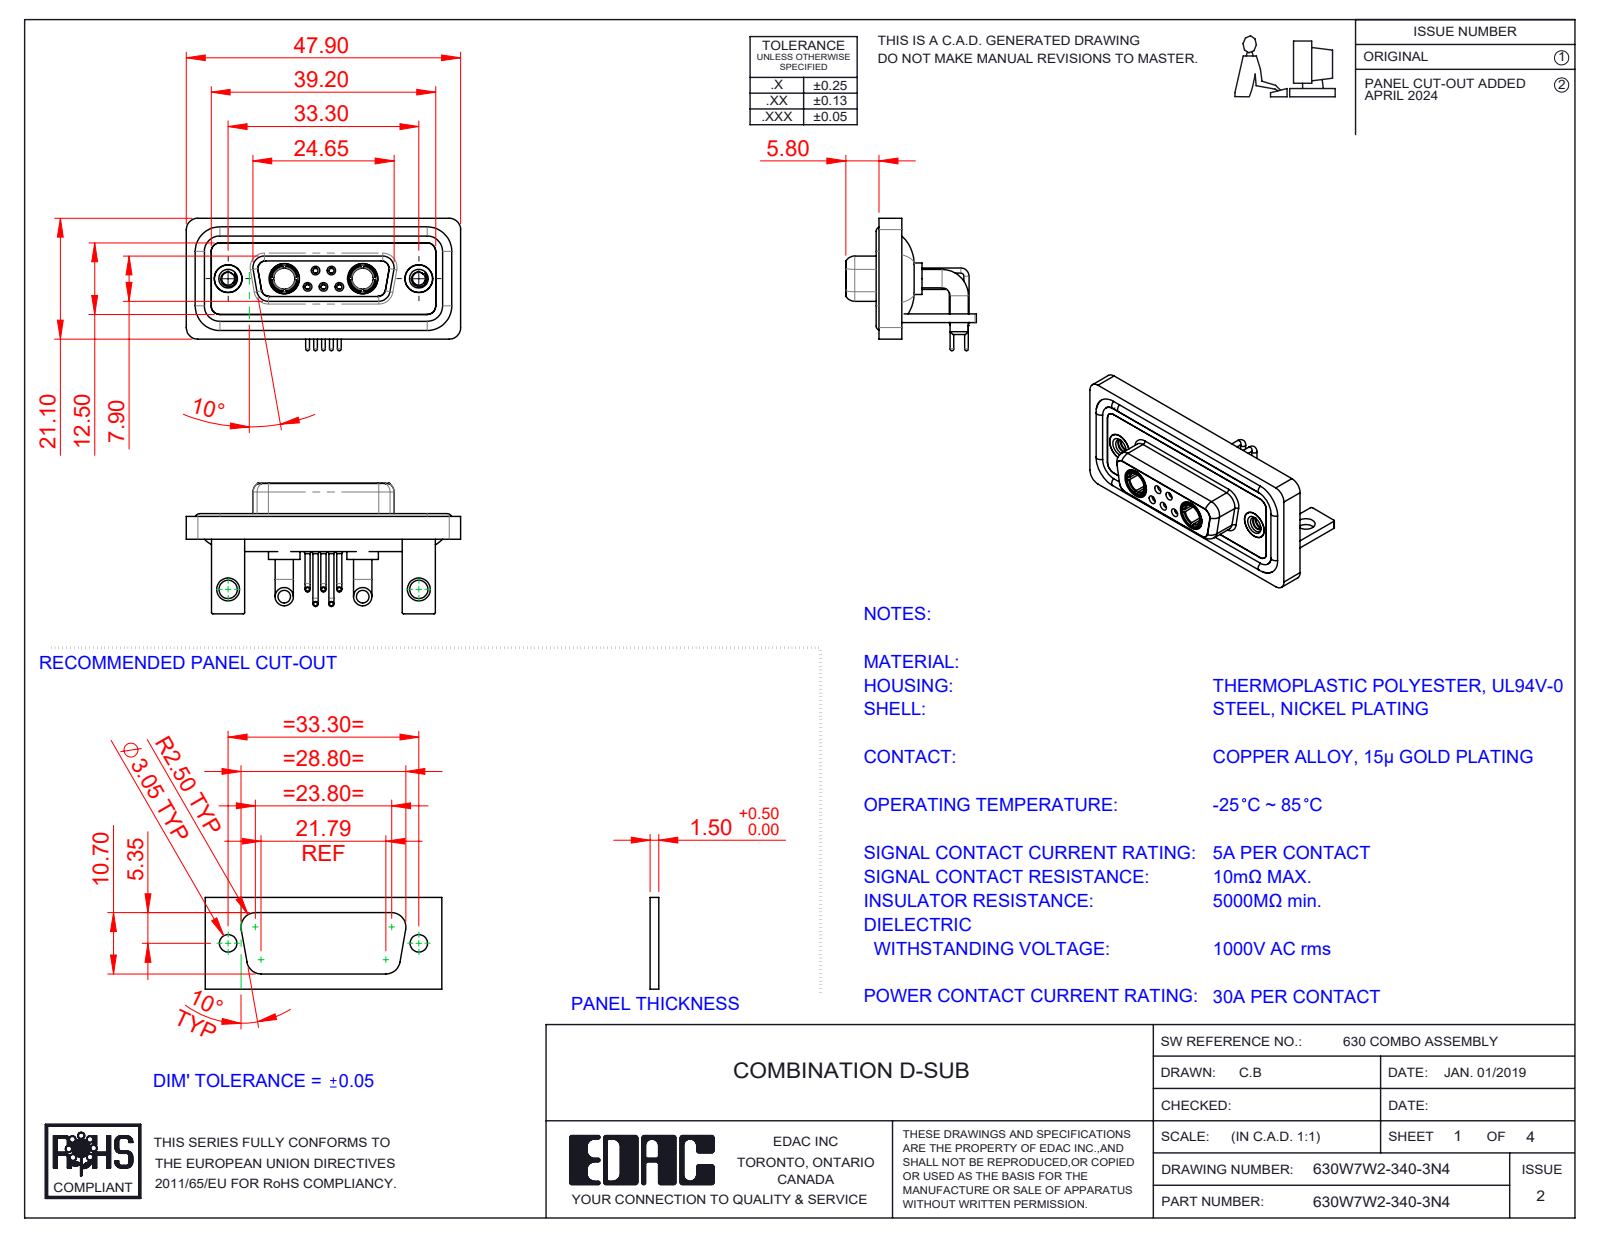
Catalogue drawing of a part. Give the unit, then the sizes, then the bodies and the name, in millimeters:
Units: millimetres
Overall size (bounding box): 47.9 × 23.12 × 22.8
Round holes (diameter × count): ⌀0.9 ×5, ⌀1.1 ×5, ⌀1.5 ×5, ⌀2 ×5, ⌀4.85 ×4, ⌀1.6 ×3, ⌀1.7 ×2, ⌀2.26 ×2, ⌀3.2 ×2, ⌀3.7 ×2, ⌀4 ×2, ⌀4.05 ×2
Round bosses / shafts (diameter × count): ⌀1.6 ×6, ⌀0.9 ×5, ⌀0.65 ×5, ⌀3.2 ×4, ⌀5.5 ×2, ⌀5.2 ×2, ⌀4.96 ×2, ⌀4.95 ×2
Partial cylindrical surfaces — rounded edges, fillets, slot ends (radius × count): R2 ×21, R1.5 ×18, R0.25 ×16, R1.35 ×12, R1.6 ×8, R0.5 ×5, R0.6 ×4, R0.65 ×4
Main face-to-face distances: 0.4, 2.9, 1.5, 1.8, 3.7, 1.1, 4.1, 1.6, 2.5, 1.4
Hole centre spacings: 3.16, 2.77, 9.8, 23.5, 33.3, 4.31, 4.33, 5.03
Volume: 6 619 mm³ · Surface area: 10 978 mm²
Bodies: 18 solids, 855 faces (258 planar, 377 cylindrical, 220 other)
Part name (STEP PRODUCT): 630W7W2-340-3N4; 630Combo Contact Row 1_50 Contacts; 630Combo Contact Row 2_50 Contacts; 630Combo Shell Rear_15 Contacts (+6 more)
STEP written by: SolidWorks 2023 (CONFIG_CONTROL_DESIGN)
